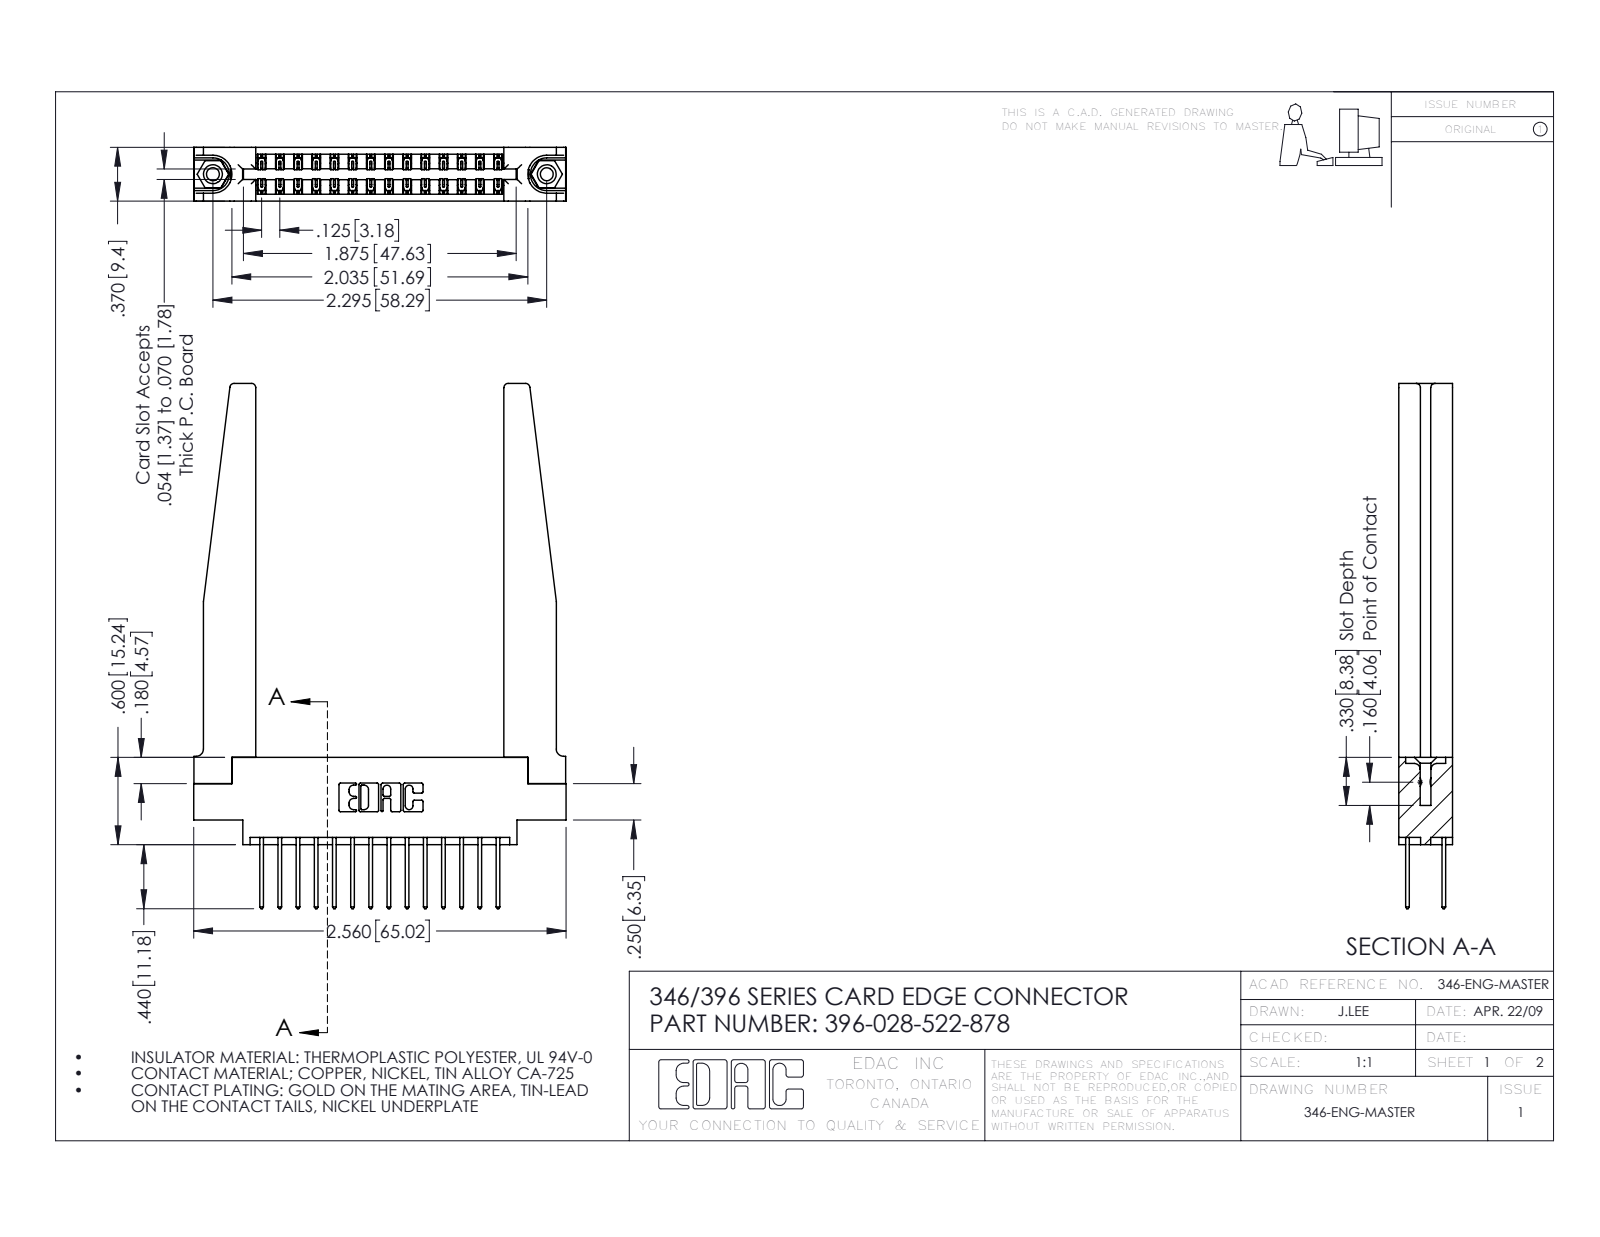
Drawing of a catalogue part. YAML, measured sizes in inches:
part_name: "345-250-001_345-250-001-102; 346 Part_0.170 Offset - 0.156 Dia-TH; 396-028-522-878; 345-292-001_345-293-122 (+1 more)"
step_written_by: "SolidWorks 2016 (CONFIG_CONTROL_DESIGN)"
units: inches
bodies: {solids: 33, faces: 1816, planar: 1202, cylindrical: 562, other: 52}
overall_size: [3.61, 2.56, 0.37]
volume: 0.79
surface_area: 23.11
round_holes:
  - {diameter: 0.089, count: 2}
  - {diameter: 0.125, count: 2}
  - {diameter: 0.156, count: 2}
  - {diameter: 0.064, count: 1}
round_bosses_or_shafts:
  - {diameter: 0.155, count: 2}
partial_cylinders:
  - {radius: 0.006, count: 42}
  - {radius: 0.01, count: 28}
  - {radius: 0.01, count: 22}
  - {radius: 0.03, count: 8}
  - {radius: 0.007, count: 6}
  - {radius: 0.031, count: 6}
  - {radius: 0.026, count: 3}
  - {radius: 0.014, count: 2}
face_to_face_distances: [0.37, 0.072, 0.048, 0.322, 0.148, 0.15, 0.25, 0.298, 0.025, 0.102]
hole_center_spacings: [0.246, 2.089, 2.295]
